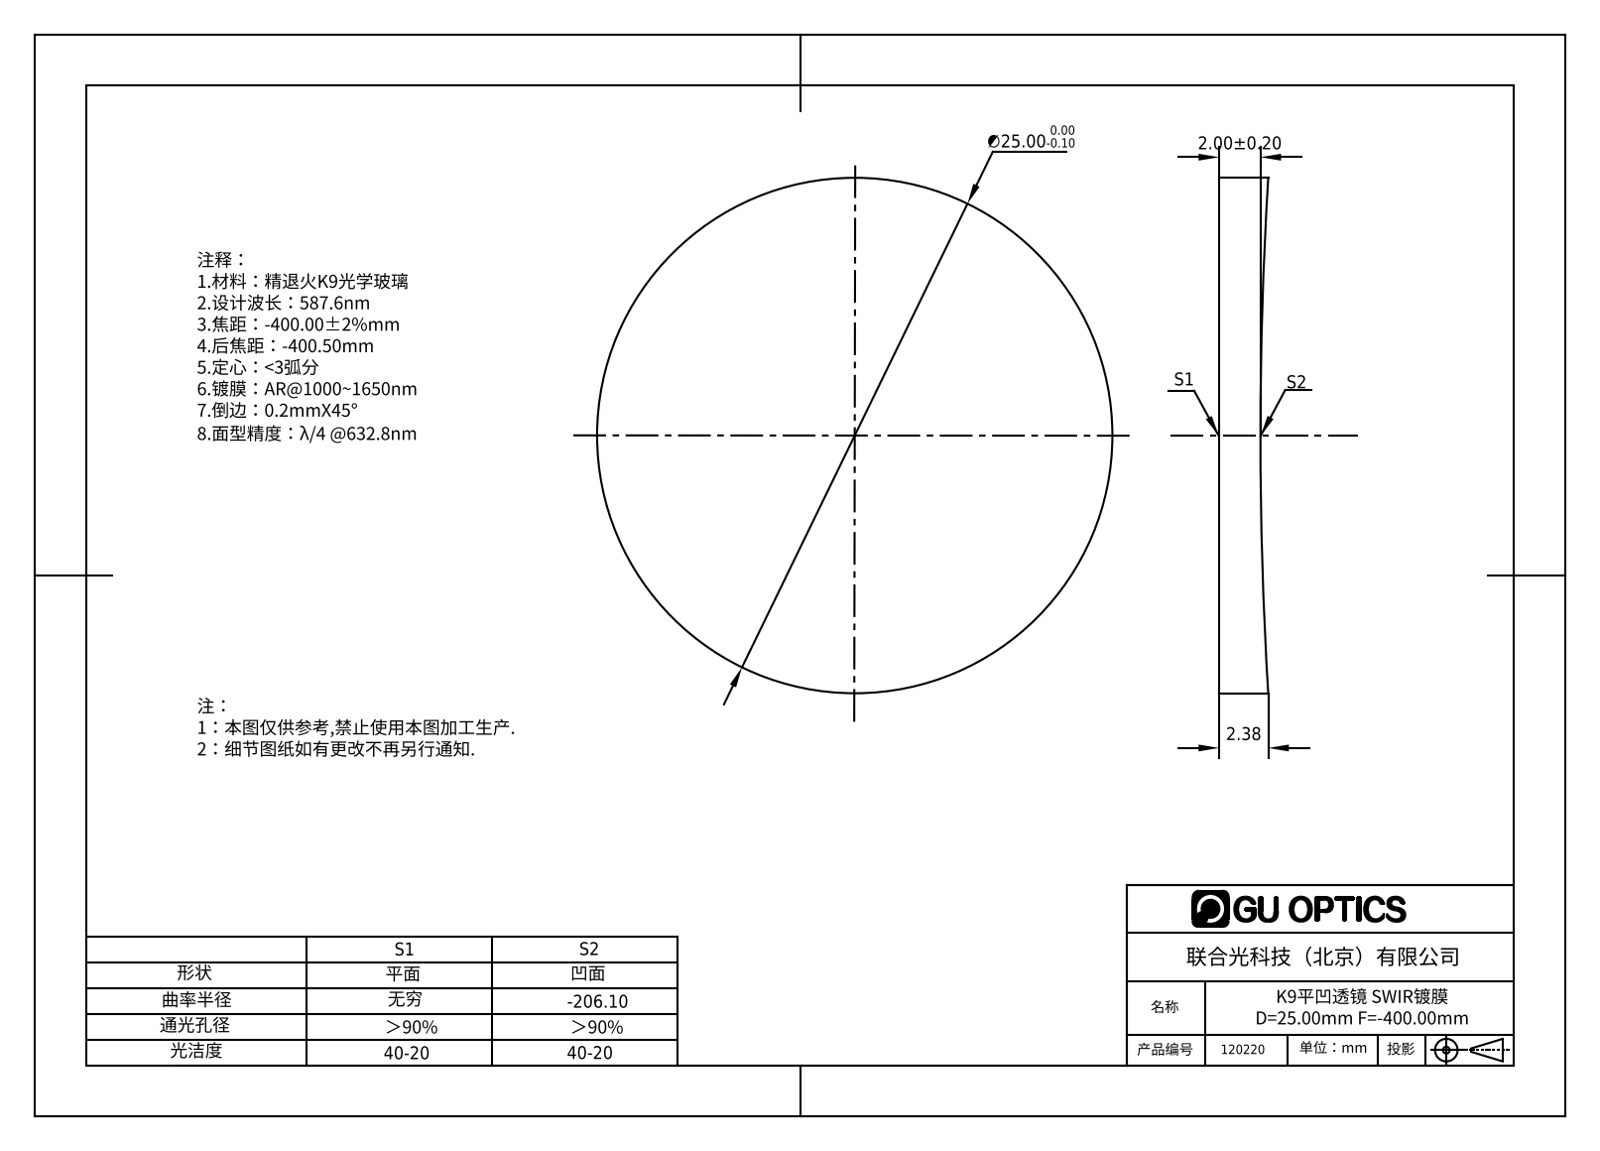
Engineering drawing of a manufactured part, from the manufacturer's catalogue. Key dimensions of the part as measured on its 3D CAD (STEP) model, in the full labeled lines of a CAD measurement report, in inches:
Part name (STEP PRODUCT): 120160
STEP written by: SolidWorks 2016 (AUTOMOTIVE_DESIGN)
Units: inches
Bodies: 1 solid, 5 faces (1 planar, 2 cylindrical, 2 other)
Overall size (bounding box): 0.984 × 0.984 × 0.094
Volume: 0.066 in³ · Surface area: 1.812 in²
Round bosses / shafts (diameter × count): ⌀0.984 ×1
